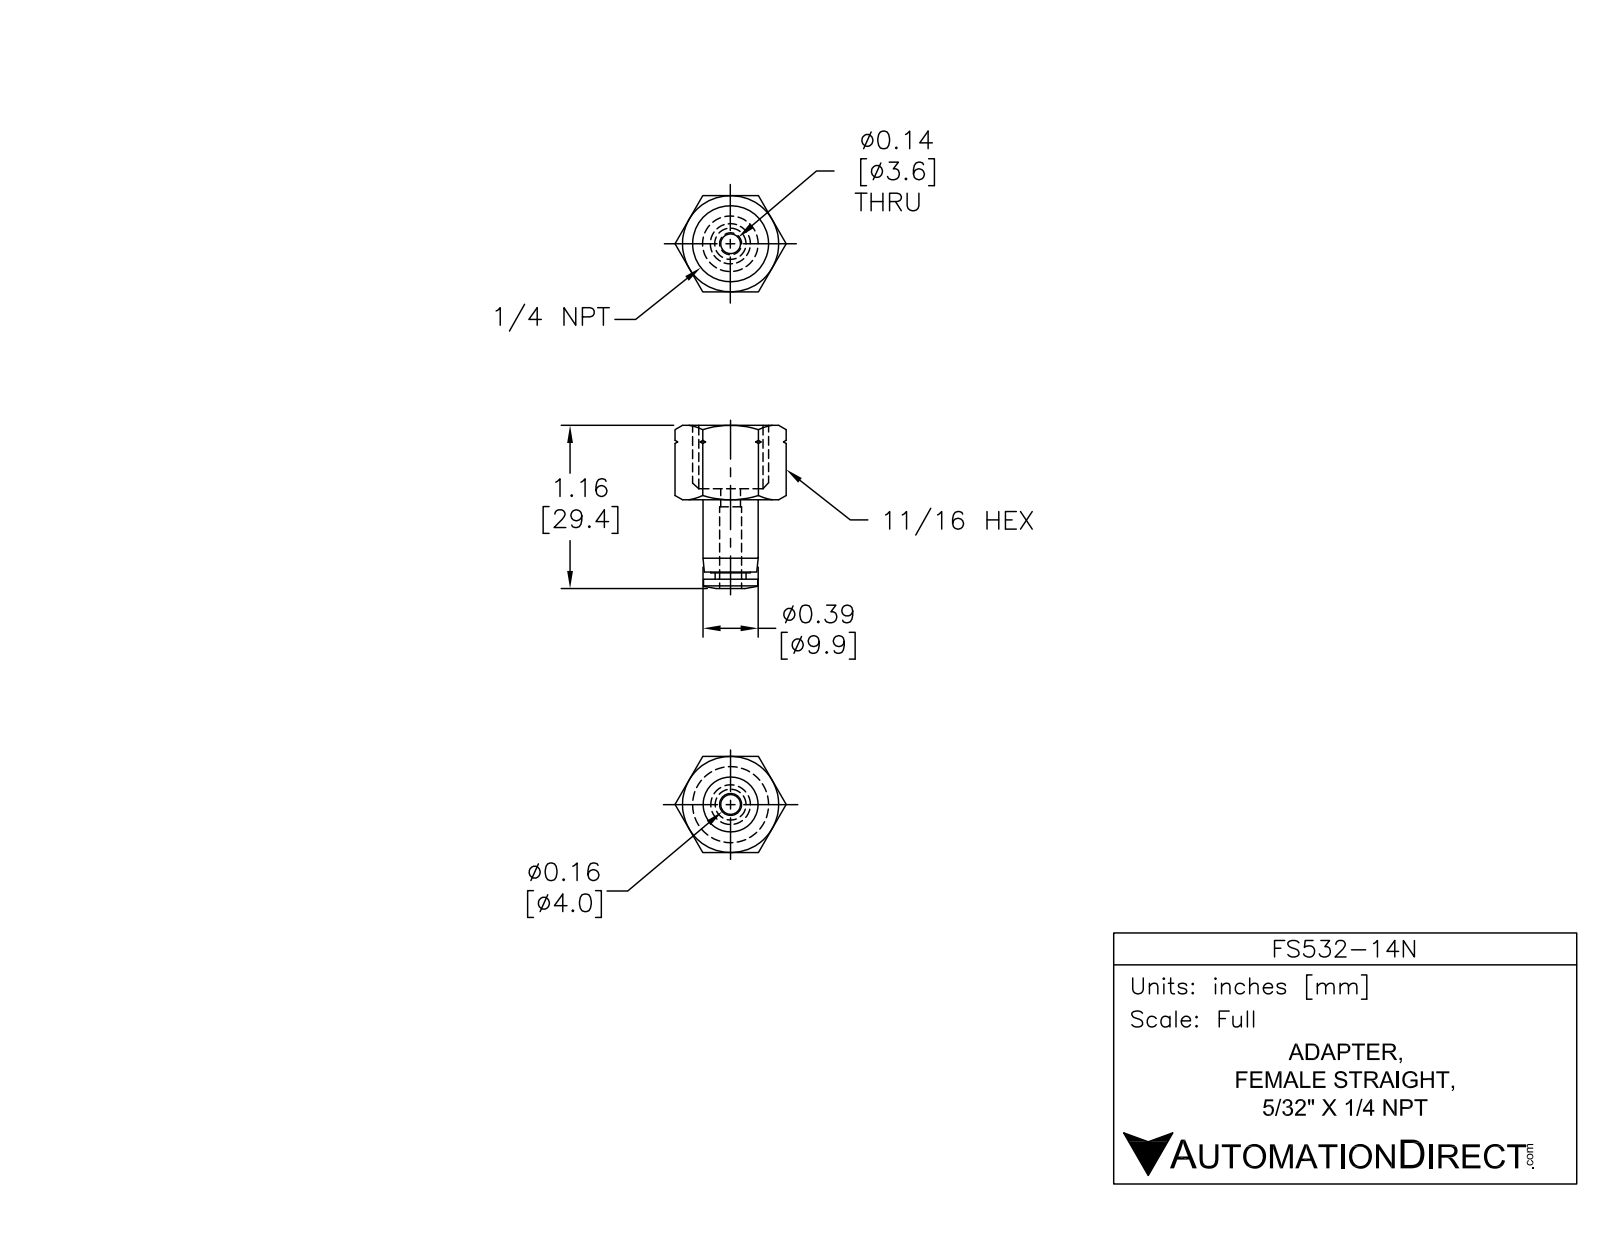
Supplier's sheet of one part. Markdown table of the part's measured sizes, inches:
| quantity | value |
| --- | --- |
| part name | FS532-14N |
| STEP written by | SolidWorks 2015 (AUTOMOTIVE_DESIGN) |
| units | inches |
| bodies | 1 solid, 61 faces (13 planar, 12 cylindrical, 36 other) |
| overall size | 1.165 × 0.794 × 0.687 |
| volume | 0.175 in³ |
| surface area | 3.989 in² |
| round holes (diameter × count) | 0.138 × 1, 0.169 × 1 |
| round bosses / shafts (diameter × count) | 0.394 × 1, 0.388 × 1, 0.283 × 1, 0.22 × 1 |
| main face-to-face distances | 0.687, 0.079, 0.453, 0.531, 1.098, 0.646, 0.567, 0.051, 0.516, 1.047 |
